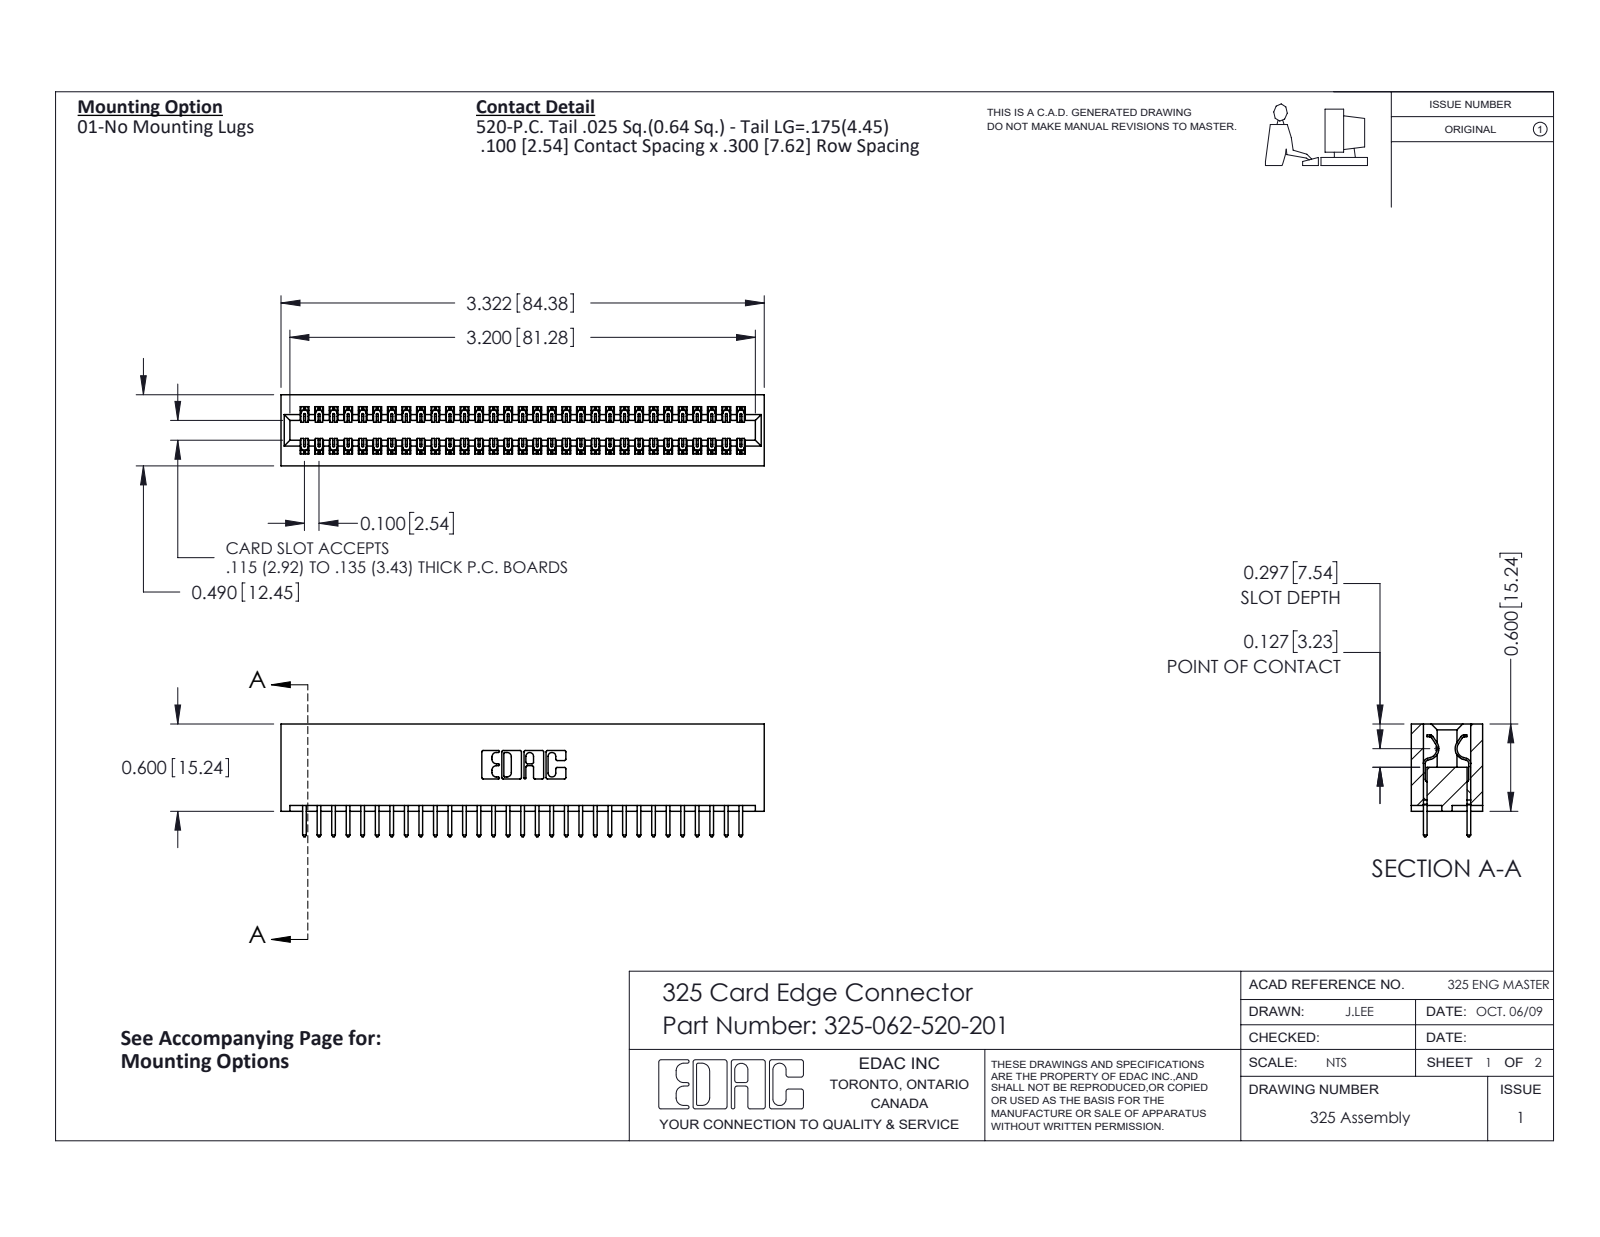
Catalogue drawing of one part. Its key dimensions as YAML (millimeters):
part_name: "325-292-001_325-293-120; 325-062-520-201; 325 Part_Lugless"
step_written_by: "SolidWorks 2016 (CONFIG_CONTROL_DESIGN)"
units: millimeters
bodies: {solids: 63, faces: 3330, planar: 2298, cylindrical: 1032, other: 0}
overall_size: [84.4, 19.7, 12.4]
volume: 11400
surface_area: 14060
partial_cylinders:
  - {radius: 0.2, count: 93}
  - {radius: 0.3, count: 62}
  - {radius: 0.3, count: 22}
  - {radius: 0.2, count: 6}
  - {radius: 0.8, count: 6}
  - {radius: 0.7, count: 3}
  - {radius: 0.4, count: 2}
  - {radius: 0.6, count: 2}
face_to_face_distances: [2.1, 10.3, 7.6, 12.4, 2.7, 9.7, 0.6, 8.3, 2.5, 7]
